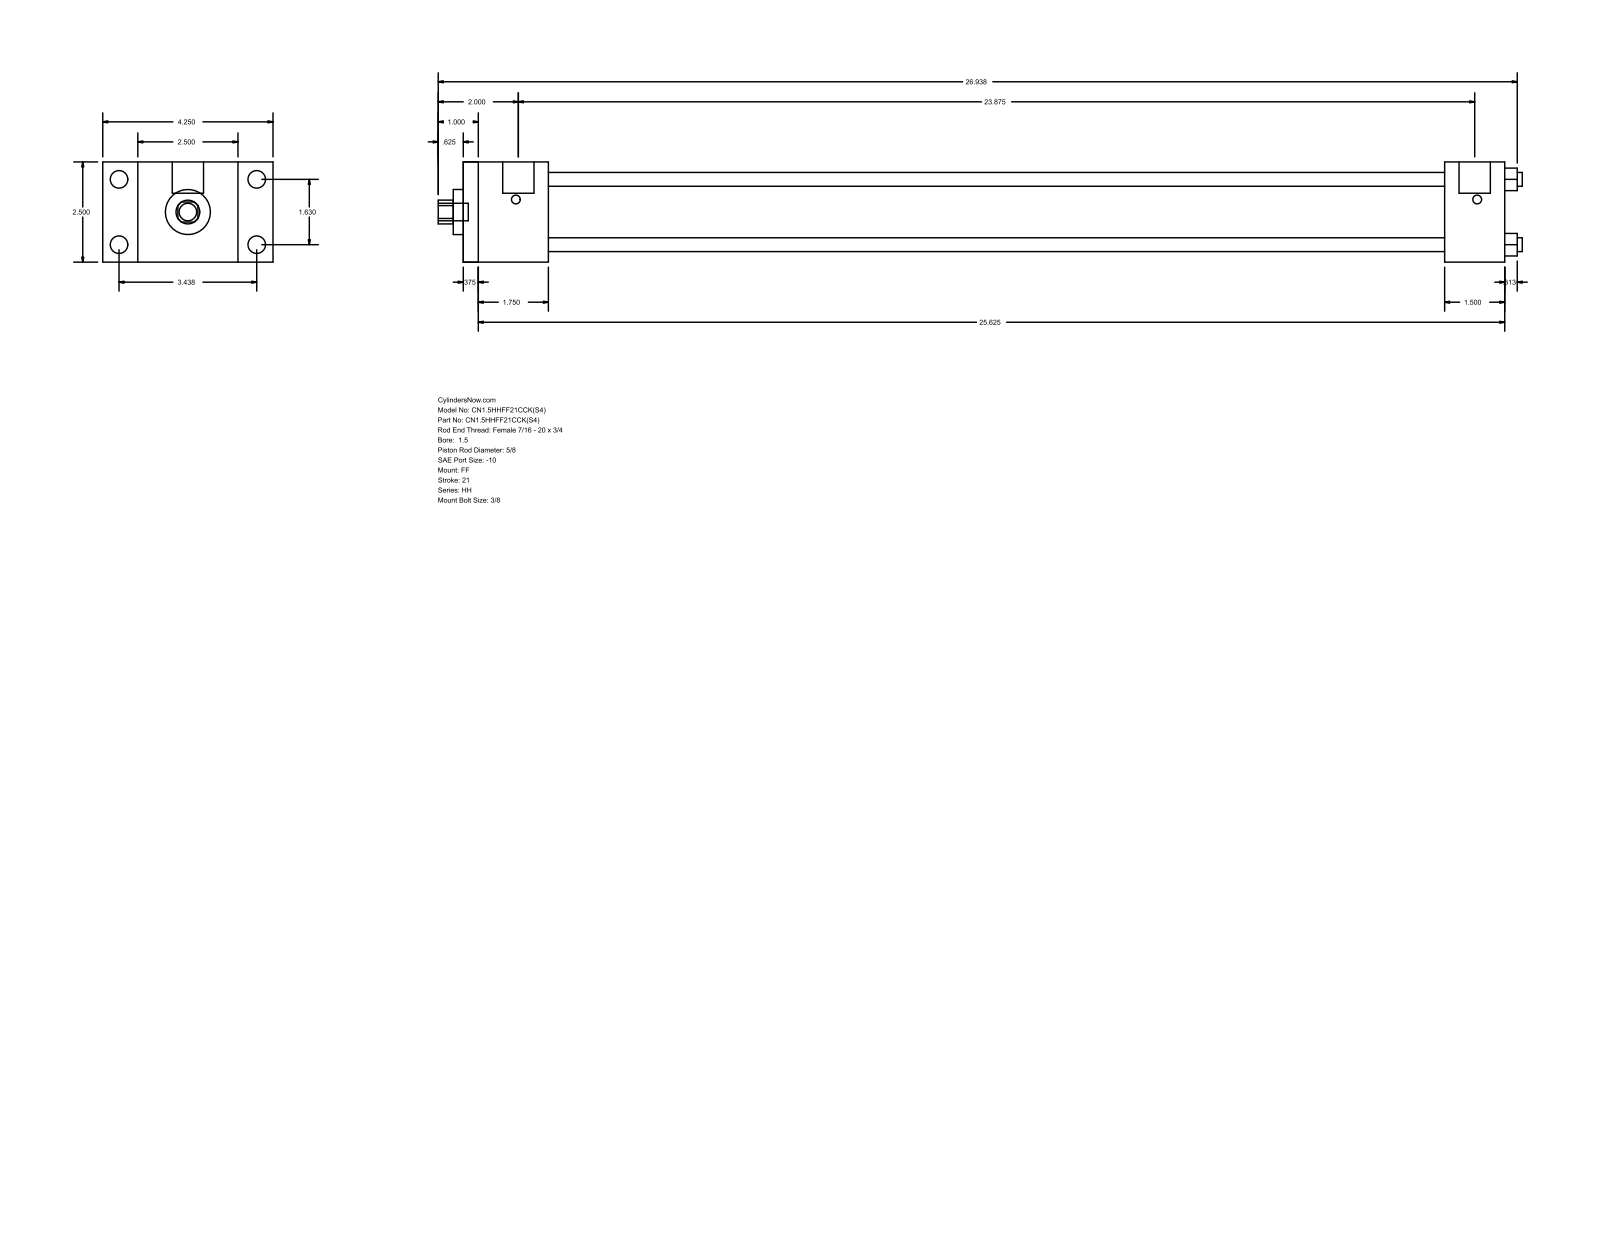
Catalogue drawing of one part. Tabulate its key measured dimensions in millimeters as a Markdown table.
| quantity | value |
| --- | --- |
| part name | HH_FF__0150_0.625 |
| STEP written by | GSSL Pune (CONFIG_CONTROL_DESIGN) |
| units | millimeters |
| bodies | 0 solids, 92 faces (64 planar, 28 cylindrical, 0 other) |
| overall size | 687.39 × 107.95 × 63.5 |
| round holes (diameter × count) | 8.76 × 4, 15.88 × 1, 28.57 × 1, 44.45 × 1 |
| round bosses / shafts (diameter × count) | 11.13 × 4, 5.56 × 4, 19.84 × 2, 11.11 × 1 |
| partial cylindrical surfaces (radius × count) | 7.54 × 1 |
| main face-to-face distances | 63.5, 660.39, 9.52, 38.1, 650.87, 53.97, 44.45, 606.42, 622.29, 612.77 |
| hole center spacings | 29.27, 41.4, 58.55 |
